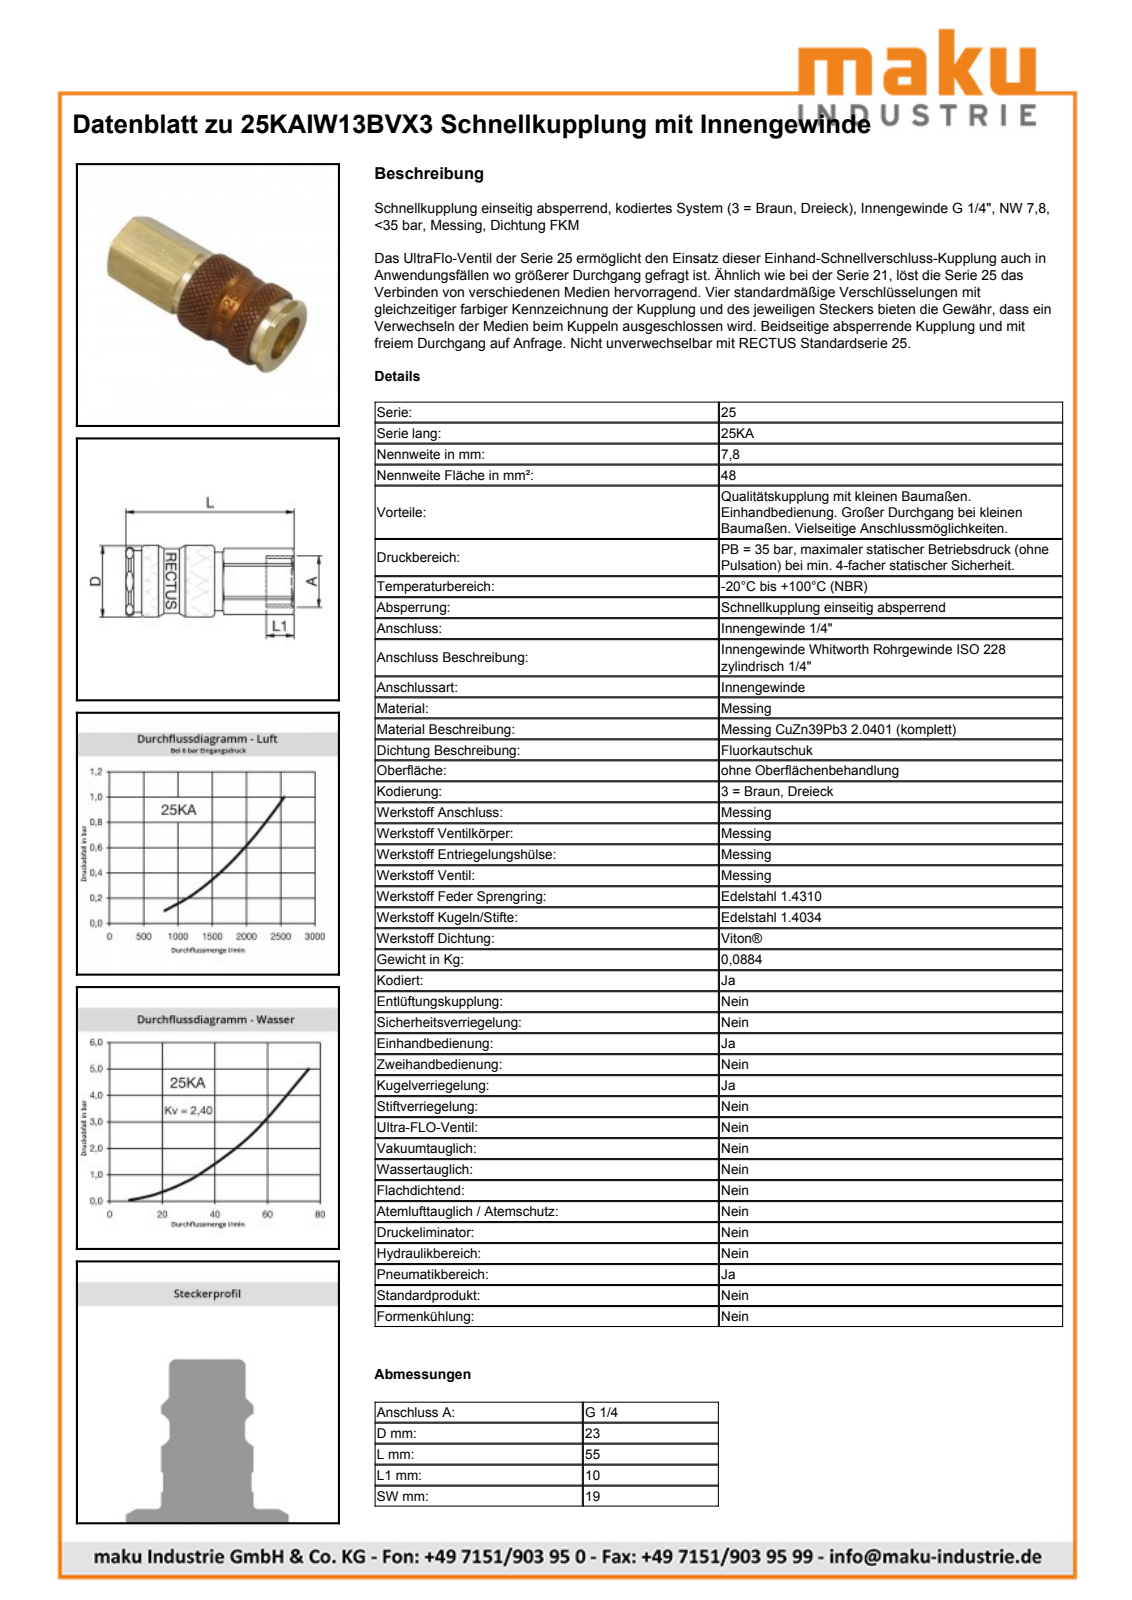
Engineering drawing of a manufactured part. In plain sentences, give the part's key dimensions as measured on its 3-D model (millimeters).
The part is named "25KAIW13BPX3". Its 3-D file was written by "Autodesk Inventor 2019 (AUTOMOTIVE_DESIGN)". It is 4 solids with 717 faces: 241 planar, 96 cylindrical and 380 other. Overall it measures 55.5 by 23.15 by 23.15 millimeters. Its volume is 16 762 cubic millimeters and its surface area 11 018 square millimeters. Round holes: 1 of diameter 9.3, 1 of diameter 11.45, 1 of diameter 14, 1 of diameter 15.1, 1 of diameter 17.25, 1 of diameter 19.35, 1 of diameter 20.05. Round bosses or shafts: 1 of diameter 23.15, 1 of diameter 21, 1 of diameter 20, 1 of diameter 18.95, 1 of diameter 16, 1 of diameter 15.3, 1 of diameter 15.17, 1 of diameter 15. Partial cylindrical surfaces (rounded edges, fillets, slot ends): 1 of radius 6.35, 1 of radius 7.9, 1 of radius 10.4, 1 of radius 10.7, 1 of radius 11. The main face-to-face distances are 19, 45.5, 6.2, 39.3, 55.5, 49.3, 10, 21, 29.1, 22.9.
